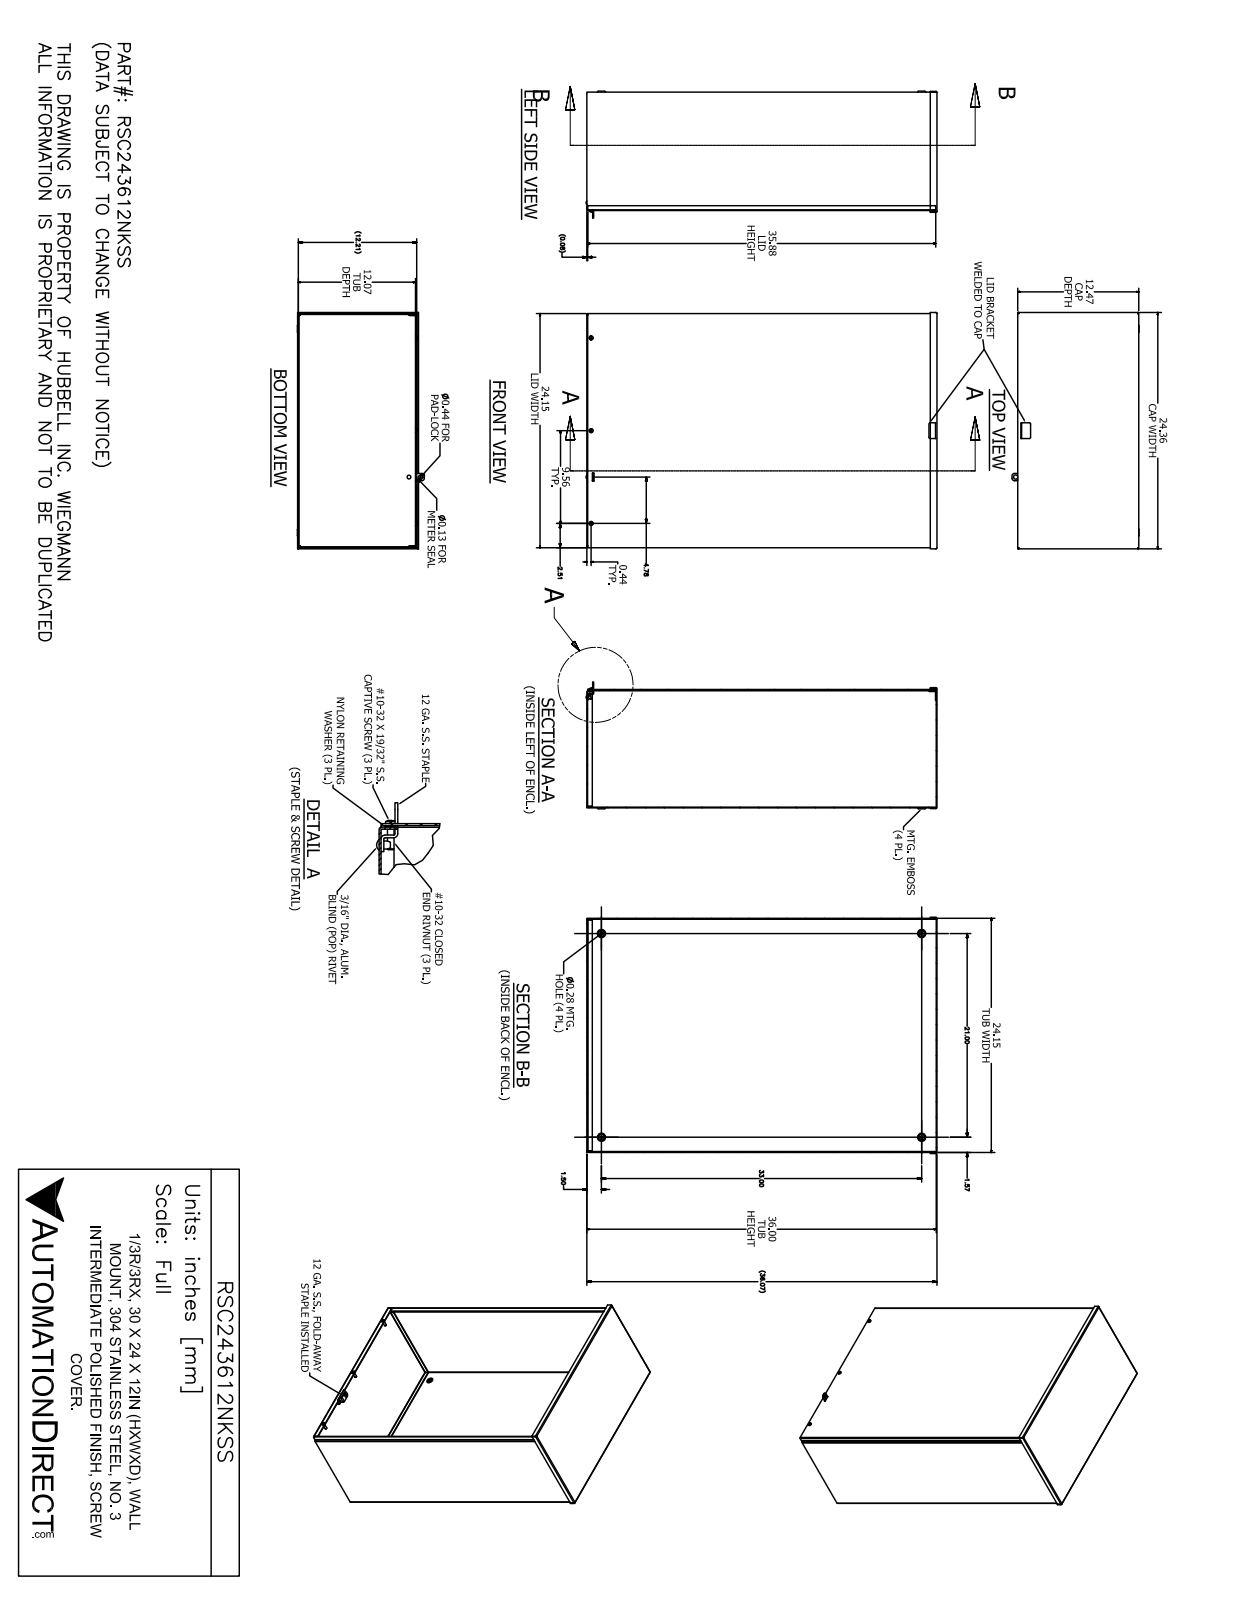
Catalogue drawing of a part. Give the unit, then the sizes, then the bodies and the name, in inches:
Units: inches
Overall size (bounding box): 36.164 × 24.359 × 13.084
Round holes (diameter × count): ⌀0.25 ×6, ⌀0.281 ×4, ⌀0.156 ×3, ⌀0.196 ×3, ⌀0.257 ×3, ⌀0.278 ×3, ⌀0.125 ×1, ⌀0.198 ×1, ⌀0.201 ×1, ⌀0.437 ×1
Round bosses / shafts (diameter × count): ⌀0.453 ×3, ⌀0.406 ×3, ⌀0.248 ×3, ⌀0.167 ×3, ⌀0.187 ×1
Partial cylindrical surfaces — rounded edges, fillets, slot ends (radius × count): R0.031 ×23, R0.105 ×17, R0.125 ×4, R0.25 ×4, R0.062 ×3, R0.089 ×3, R0.047 ×2, R0.05 ×2
Main face-to-face distances: 0.074, 12.132, 12.206, 12.058, 24.074, 36, 24.148, 24, 36.074, 35.926
Hole centre spacings: 9.563, 36.433, 35.156, 1.417, 1.441, 10.554, 10.557, 19.125
Volume: 244.5 in³ · Surface area: 6 644 in²
Bodies: 16 solids, 458 faces (237 planar, 113 cylindrical, 108 other)
Part name (STEP PRODUCT): RSC243612NKSS
STEP written by: SolidWorks 2017 (AUTOMOTIVE_DESIGN)
